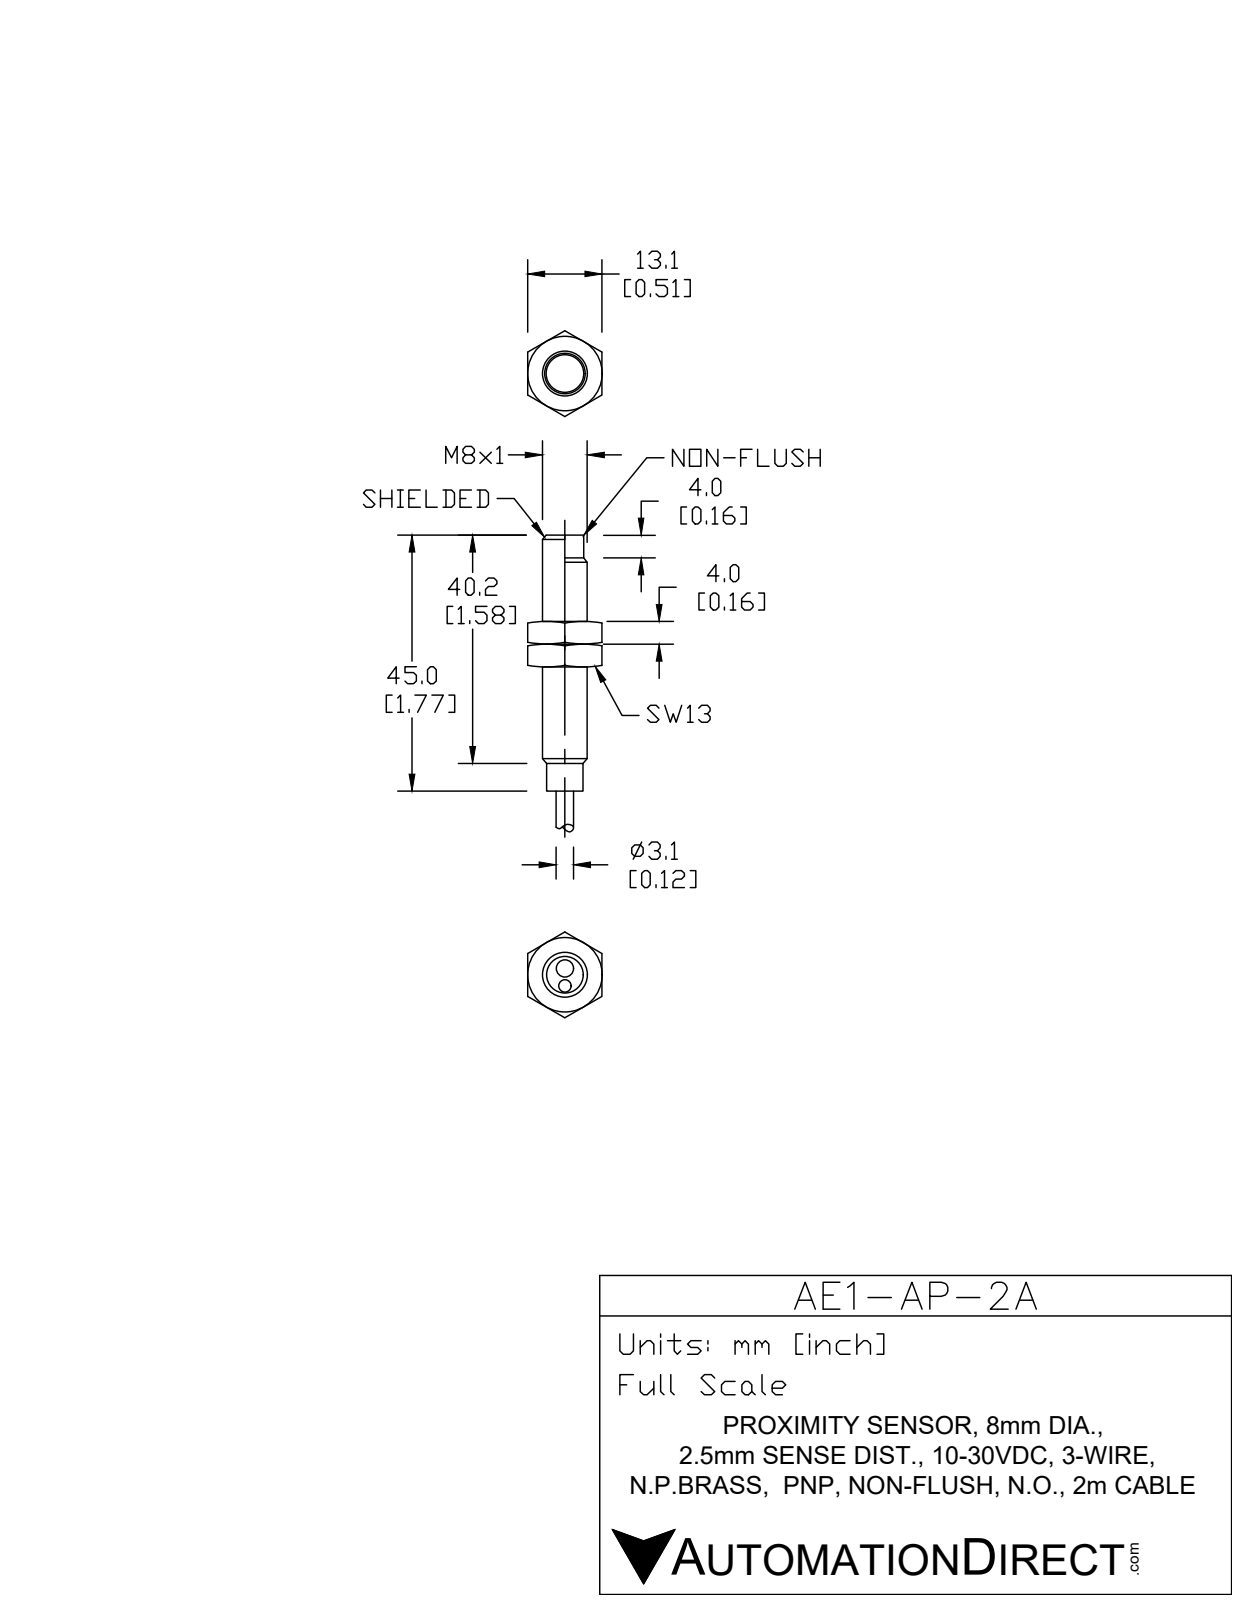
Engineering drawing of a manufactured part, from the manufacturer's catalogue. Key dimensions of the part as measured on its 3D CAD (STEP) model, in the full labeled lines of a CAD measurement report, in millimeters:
Part name (STEP PRODUCT): AE1-AP-2A
STEP written by: SolidWorks 2017 (AUTOMOTIVE_DESIGN)
Units: millimetres
Bodies: 4 solids, 30 faces (10 planar, 12 cylindrical, 8 other)
Overall size (bounding box): 82.6 × 8 × 8
Volume: 2 380 mm³ · Surface area: 1 726 mm²
Round holes (diameter × count): ⌀3.1 ×1, ⌀5.8 ×1
Round bosses / shafts (diameter × count): ⌀8 ×1, ⌀6.5 ×1, ⌀6.5 ×1
Main face-to-face distances: 36.2, 4, 40.2, 44.5, 40.5, 4.3, 2.4, 42.6, 38.6, 1.9
Hole centre spacings: 1.1
